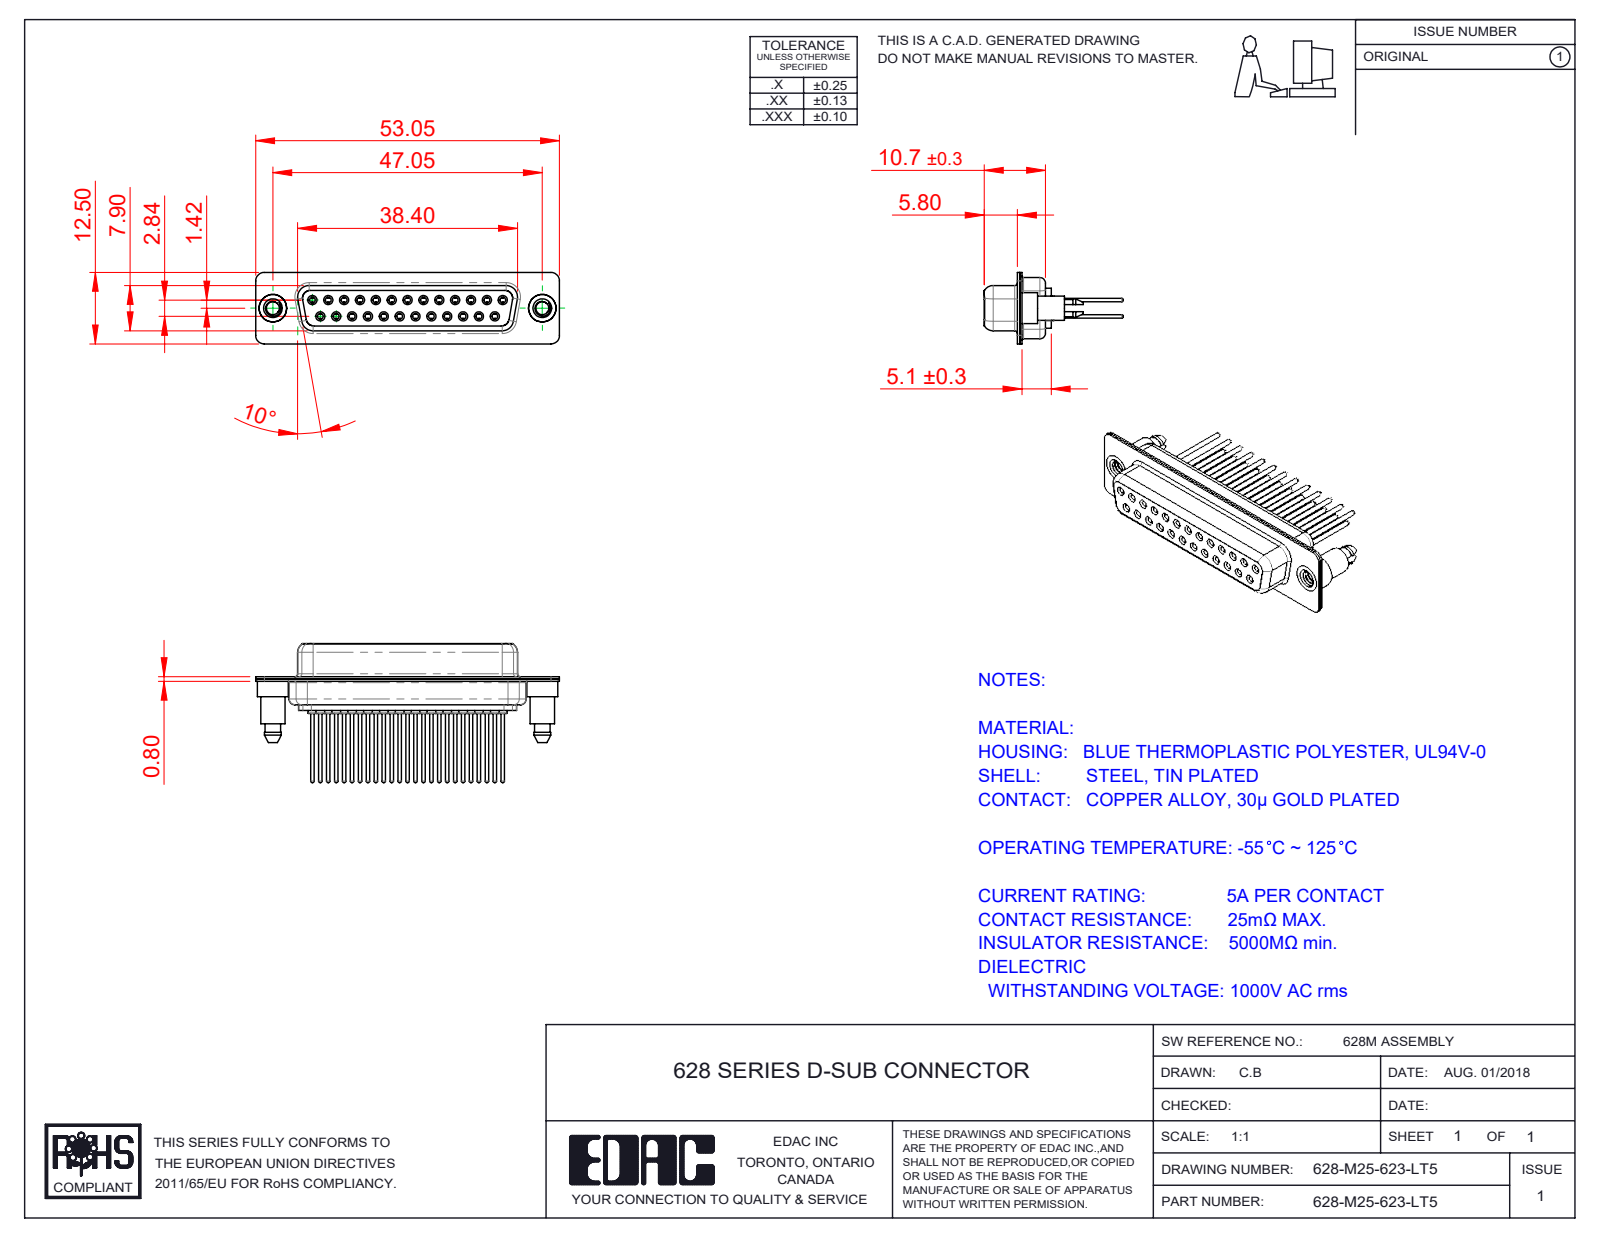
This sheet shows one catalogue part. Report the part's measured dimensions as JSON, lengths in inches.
{"part_name": "628M Contact Row 1_23; 628M 4-40 Threaded Boardlock; 628M Shell Front_25 Contacts; 628-M25-623-LT5 (+3 more)", "step_written_by": "SolidWorks 2020 (CONFIG_CONTROL_DESIGN)", "units": "inches", "bodies": {"solids": 30, "faces": 1704, "planar": 458, "cylindrical": 644, "other": 602}, "overall_size": [2.089, 0.956, 0.492], "volume_in3": 0.239, "surface_area_in2": 15.18, "round_holes": [[0.039, 25], [0.043, 25], [0.067, 25], [0.071, 25], [0.079, 25], [0.089, 2], [0.157, 2], [0.189, 2]], "round_bosses_or_shafts": [[0.087, 25], [0.063, 25], [0.059, 25], [0.024, 25], [0.213, 2], [0.193, 2], [0.167, 2]], "partial_cylinders_radius": [[0.059, 18], [0.079, 12], [0.063, 10], [0.053, 8], [0.01, 4], [0.02, 4], [0.024, 4], [0.026, 4]], "face_to_face_distances": [0.016, 0.055, 0.018, 0.333, 0.35, 0.071, 0.244, 0.278, 0.039, 0.073], "hole_center_spacings": [0.124, 0.109, 0.218, 0.327, 0.436, 0.545, 0.198, 0.295]}
